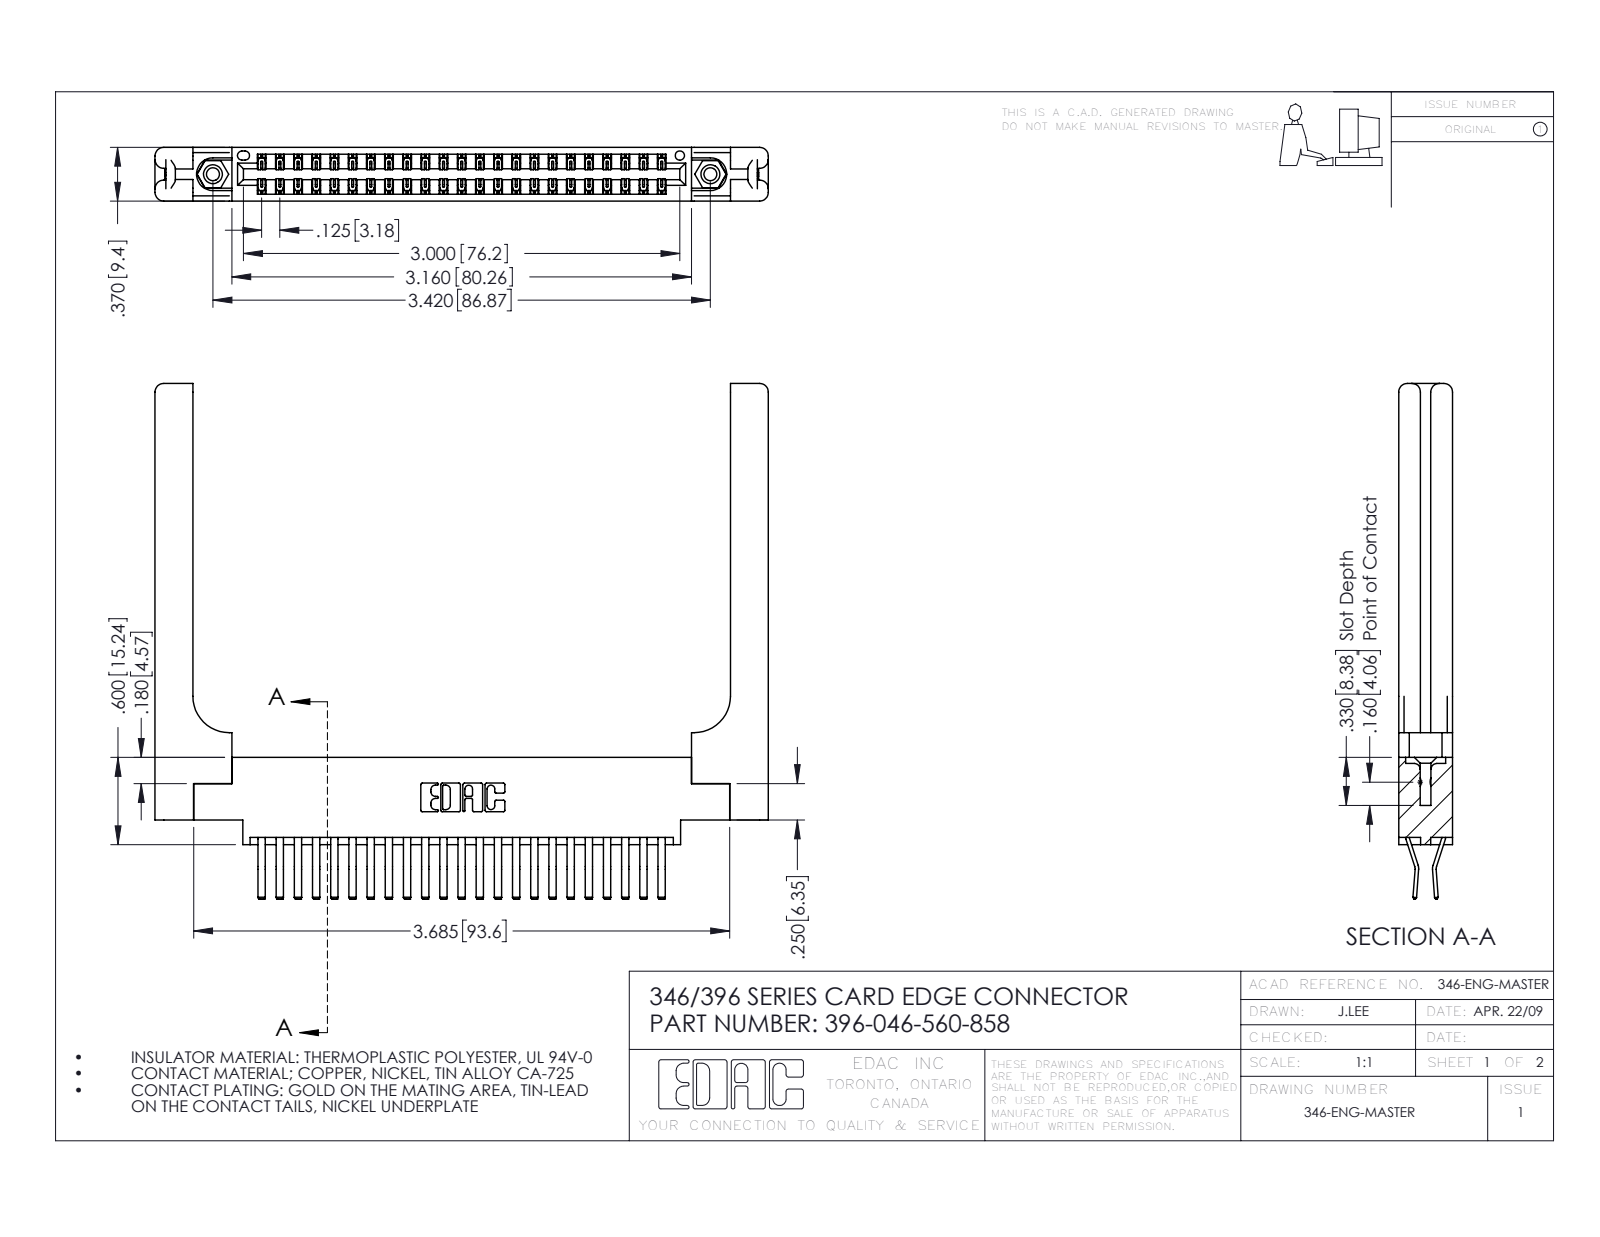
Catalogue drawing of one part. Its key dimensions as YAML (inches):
part_name: "345-250-001_345-250-001-102; 346-220-058_345-220-058; 345-292-001_560 Tail; 346 Part_0.170 Offset - 0.156 Dia-TH (+1 more)"
step_written_by: "SolidWorks 2016 (CONFIG_CONTROL_DESIGN)"
units: inches
bodies: {solids: 51, faces: 2866, planar: 1838, cylindrical: 968, other: 60}
overall_size: [4.216, 3.545, 0.37]
volume: 1.095
surface_area: 31.02
round_holes:
  - {diameter: 0.089, count: 2}
  - {diameter: 0.125, count: 2}
  - {diameter: 0.156, count: 2}
  - {diameter: 0.064, count: 1}
round_bosses_or_shafts:
  - {diameter: 0.155, count: 2}
partial_cylinders:
  - {radius: 0.006, count: 69}
  - {radius: 0.01, count: 22}
  - {radius: 0.06, count: 16}
  - {radius: 0.007, count: 6}
  - {radius: 0.031, count: 6}
  - {radius: 0.026, count: 3}
  - {radius: 0.01, count: 2}
  - {radius: 0.014, count: 2}
face_to_face_distances: [0.37, 0.072, 0.048, 0.322, 0.148, 0.15, 0.025, 0.25, 0.298, 0.077]
hole_center_spacings: [0.246, 3.212, 3.42]
